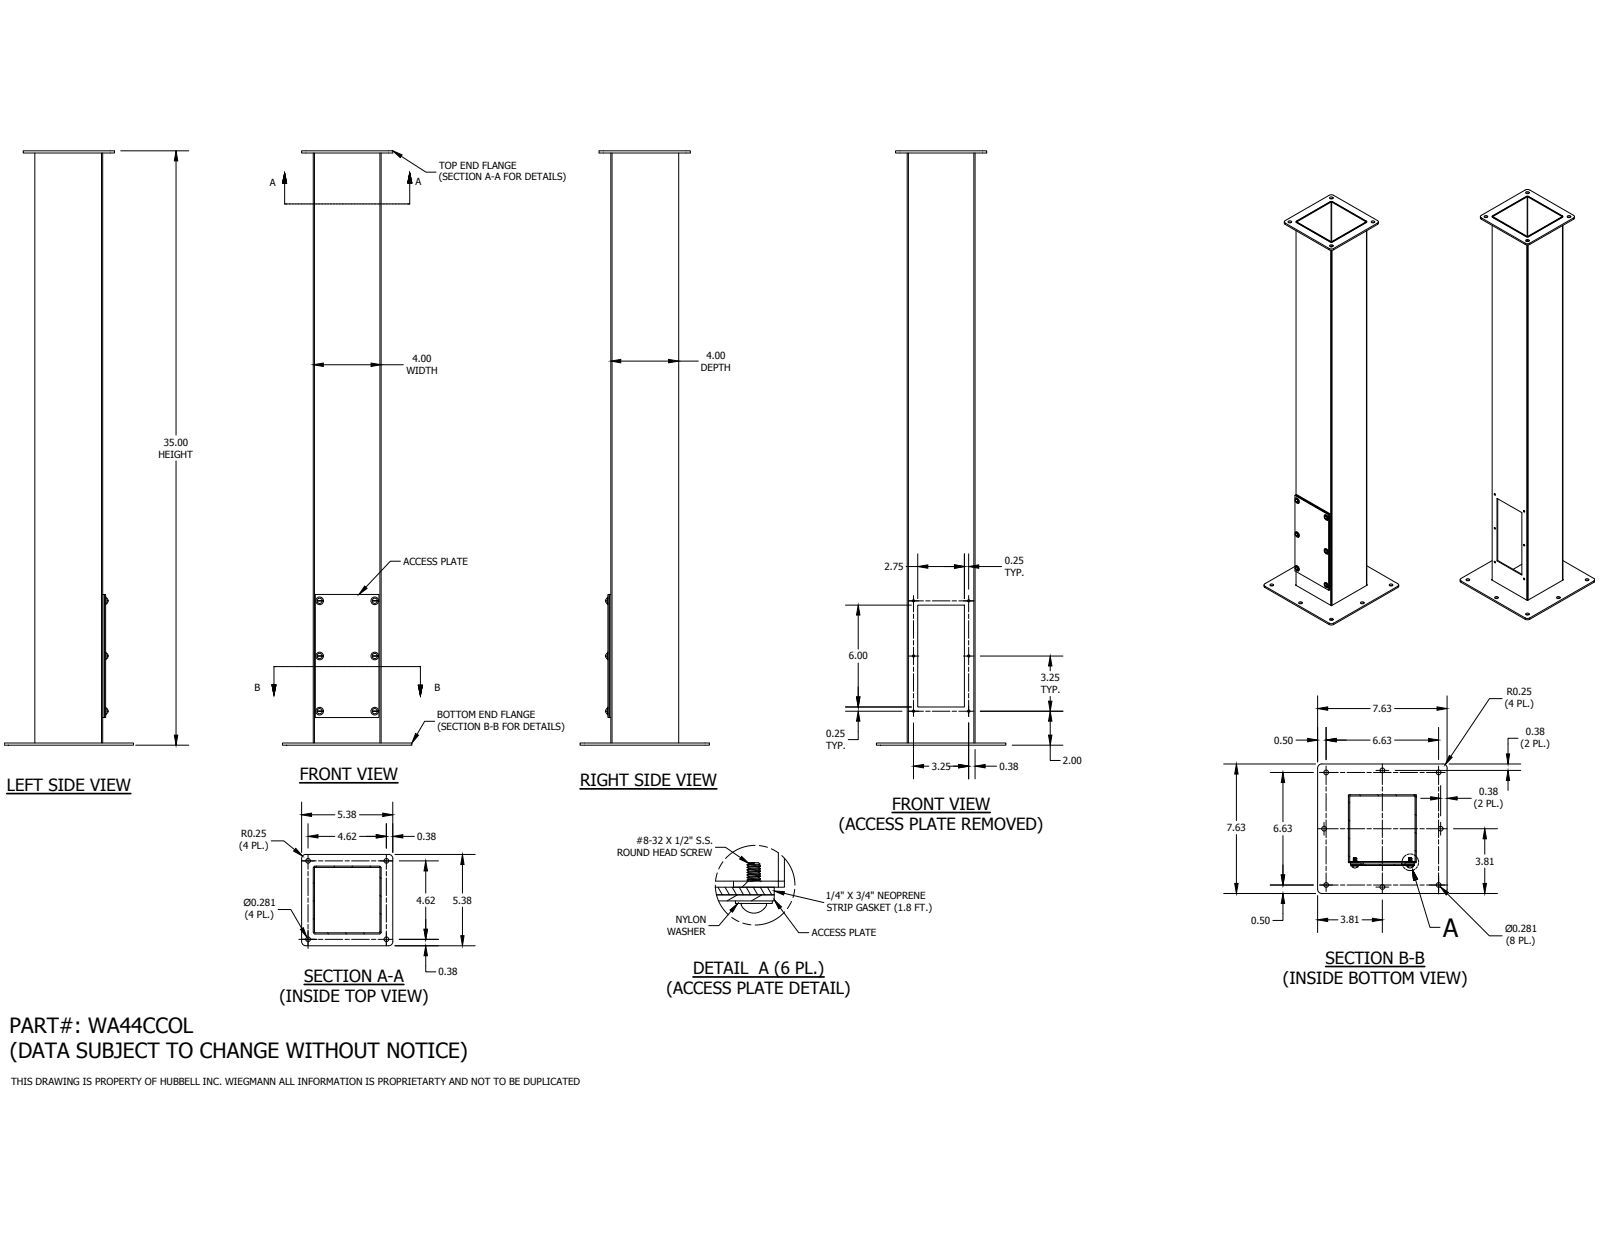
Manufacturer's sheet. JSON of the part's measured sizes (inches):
{"part_name": "WA44CCOLFRONT; WA44CCOLBLR; WA44CCOLBASERING; WA44CCOLCOVER (+5 more)", "step_written_by": "Autodesk Inventor 2016 (AUTOMOTIVE_DESIGN)", "units": "inches", "bodies": {"solids": 24, "faces": 320, "planar": 190, "cylindrical": 94, "other": 36}, "overall_size": [35, 7.625, 7.625], "volume_in3": 49.11, "surface_area_in2": 1280, "round_holes": [[0.281, 12], [0.14, 6], [0.25, 6], [0.278, 6]], "round_bosses_or_shafts": [[0.453, 6], [0.309, 6], [0.164, 6], [0.123, 6]], "partial_cylinders_radius": [[0.25, 8], [0.089, 6], [0.125, 4], [0.031, 2], [0.105, 2]], "face_to_face_distances": [0.074, 3.926, 4, 3.852, 4.094, 0.168, 0.125, 4.02, 0.094, 4.168], "hole_center_spacings": [3.25, 2.569, 3.315, 4.596, 5.709, 6.191, 7.519, 6.5]}
